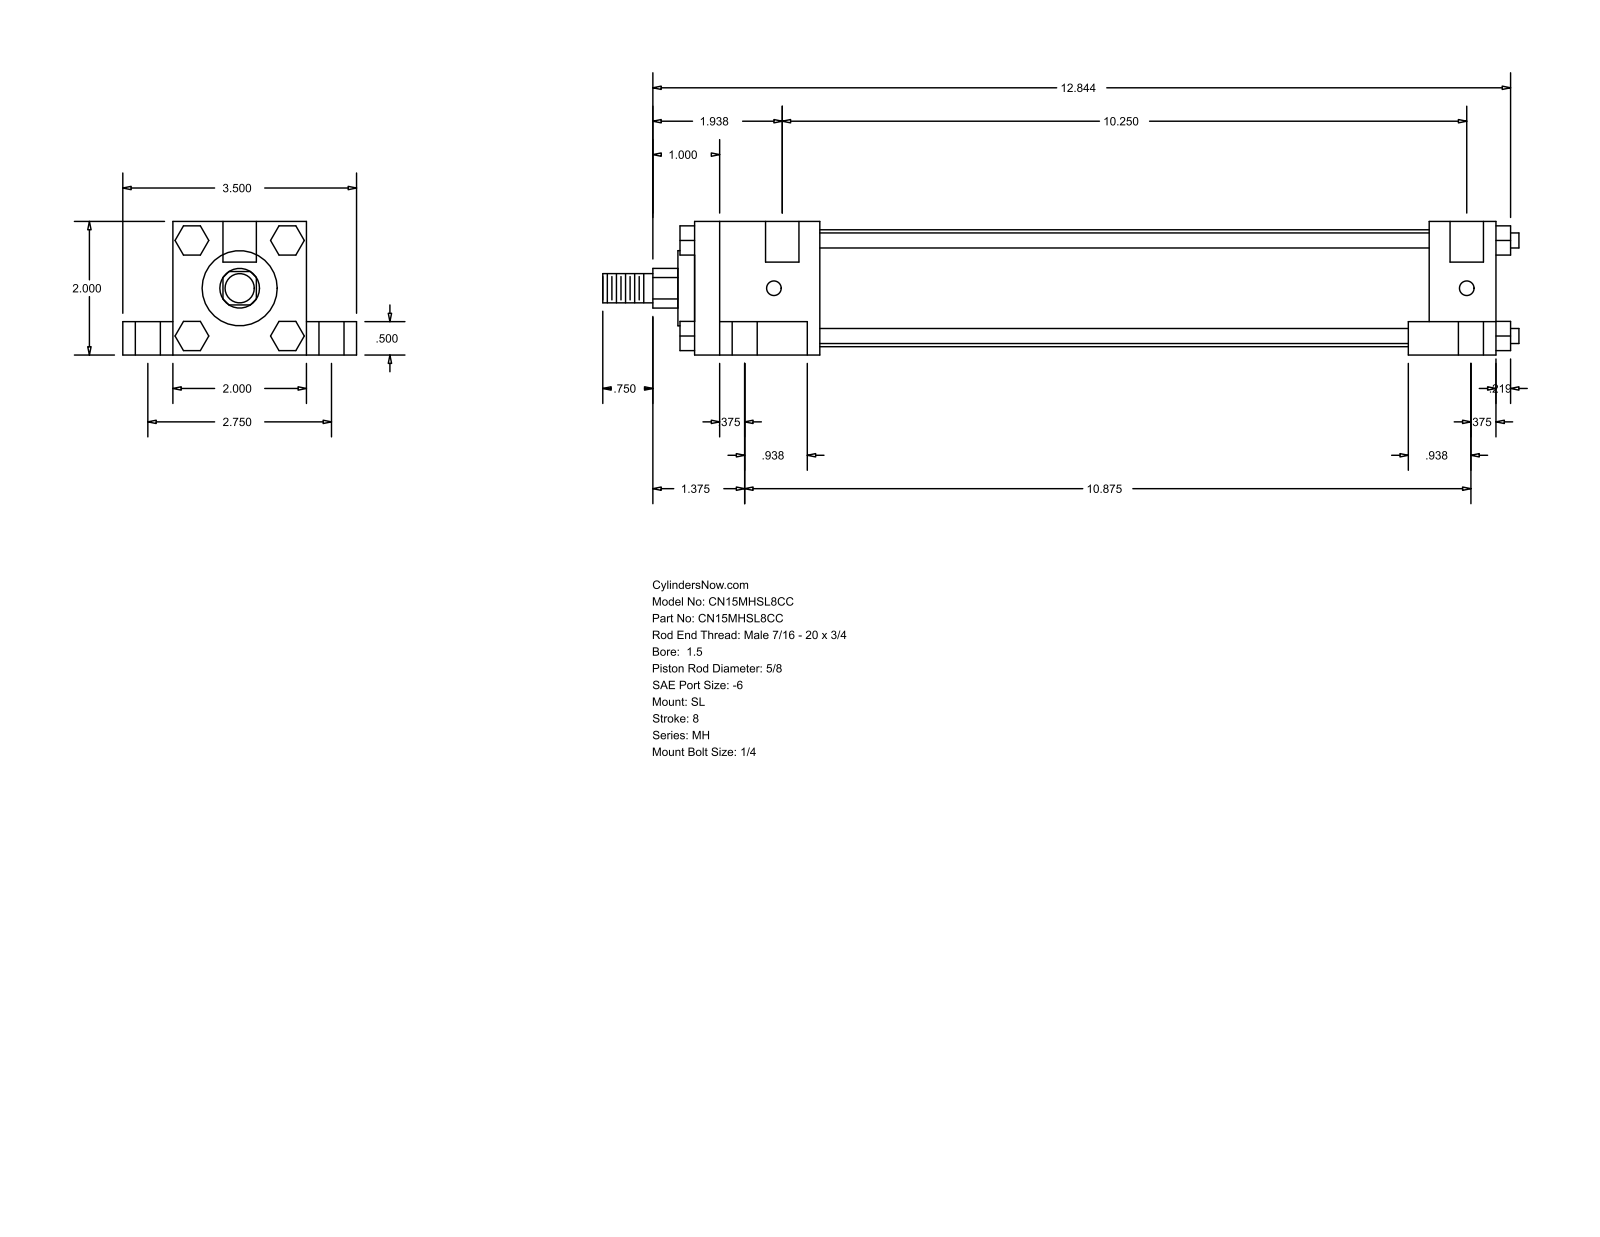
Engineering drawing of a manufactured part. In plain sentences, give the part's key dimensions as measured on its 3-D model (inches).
The part is named "MH_SL__0150_0.625". Its 3-D file was written by "GSSL Pune (CONFIG_CONTROL_DESIGN)". It is 0 solids with 148 faces: 112 planar, 36 cylindrical and 0 other. Overall it measures 13.719 by 3.5 by 2 inches. Round holes: 4 of diameter 0.219, 4 of diameter 0.375, 4 of diameter 0.625, 2 of diameter 0.5. Round bosses or shafts: 4 of diameter 0.225, 1 of diameter 1.75, 1 of diameter 1.125, 1 of diameter 0.625, 1 of diameter 0.437. Partial cylindrical surfaces (rounded edges, fillets, slot ends): 1 of radius 0.297. The main face-to-face distances are 2, 1.5, 0.75, 0.5, 2.75, 12, 0.375, 1.313, 10.313, 11. The hole center spacings are 1.376, 1.443, 1.485, 2.75, 10.375, 10.404, 10.528, 10.875.
